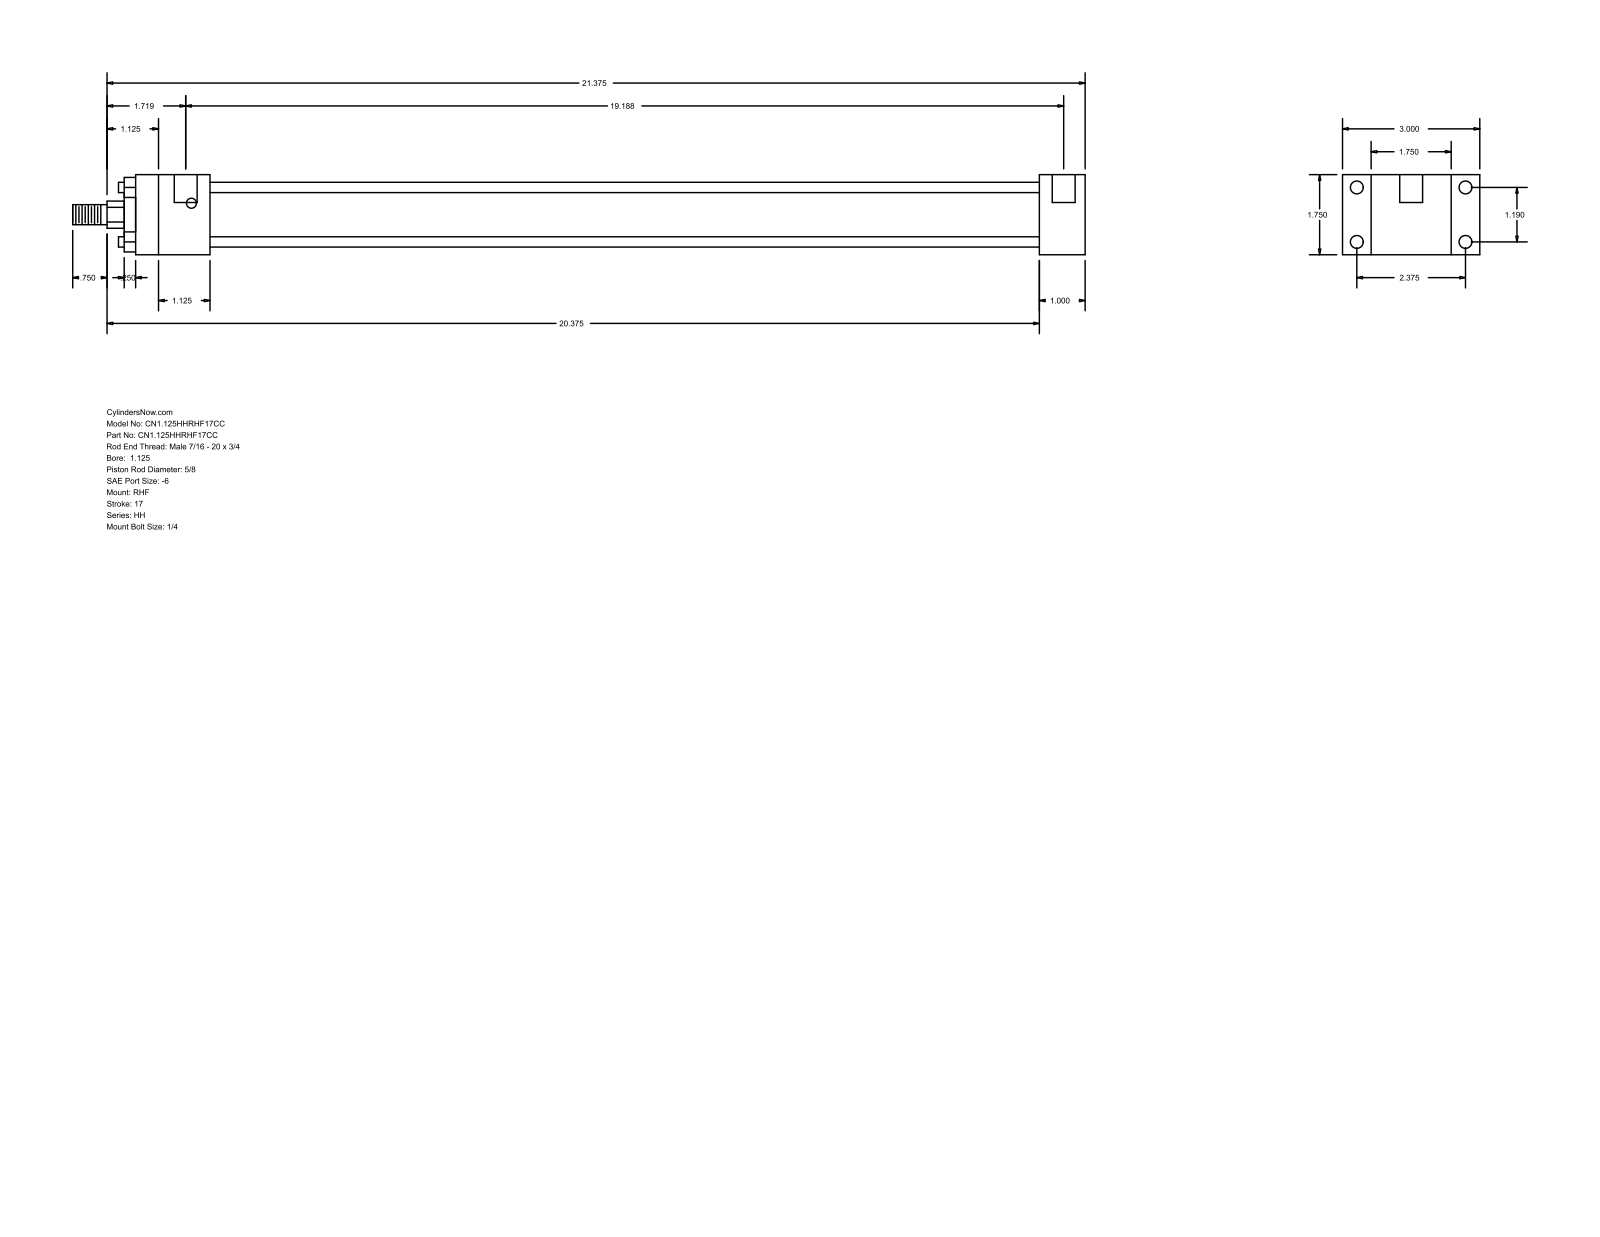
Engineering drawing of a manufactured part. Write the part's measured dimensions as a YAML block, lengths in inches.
part_name: "HH_RHF__0112_0.625"
step_written_by: "GSSL Pune (CONFIG_CONTROL_DESIGN)"
units: inches
bodies: {solids: 0, faces: 88, planar: 60, cylindrical: 28, other: 0}
overall_size: [22.125, 3, 1.75]
round_holes:
  - {diameter: 0.219, count: 4}
  - {diameter: 0.281, count: 4}
  - {diameter: 0.5, count: 2}
round_bosses_or_shafts:
  - {diameter: 0.225, count: 4}
  - {diameter: 1.375, count: 1}
  - {diameter: 1.125, count: 1}
  - {diameter: 0.625, count: 1}
  - {diameter: 0.437, count: 1}
partial_cylinders:
  - {radius: 0.297, count: 1}
face_to_face_distances: [1.75, 0.625, 1, 2.375, 3, 18.125, 19.125, 1.625, 19.75, 20.75]
hole_center_spacings: [1.19, 2.375, 2.656, 19.063, 0.125, 19.187]
